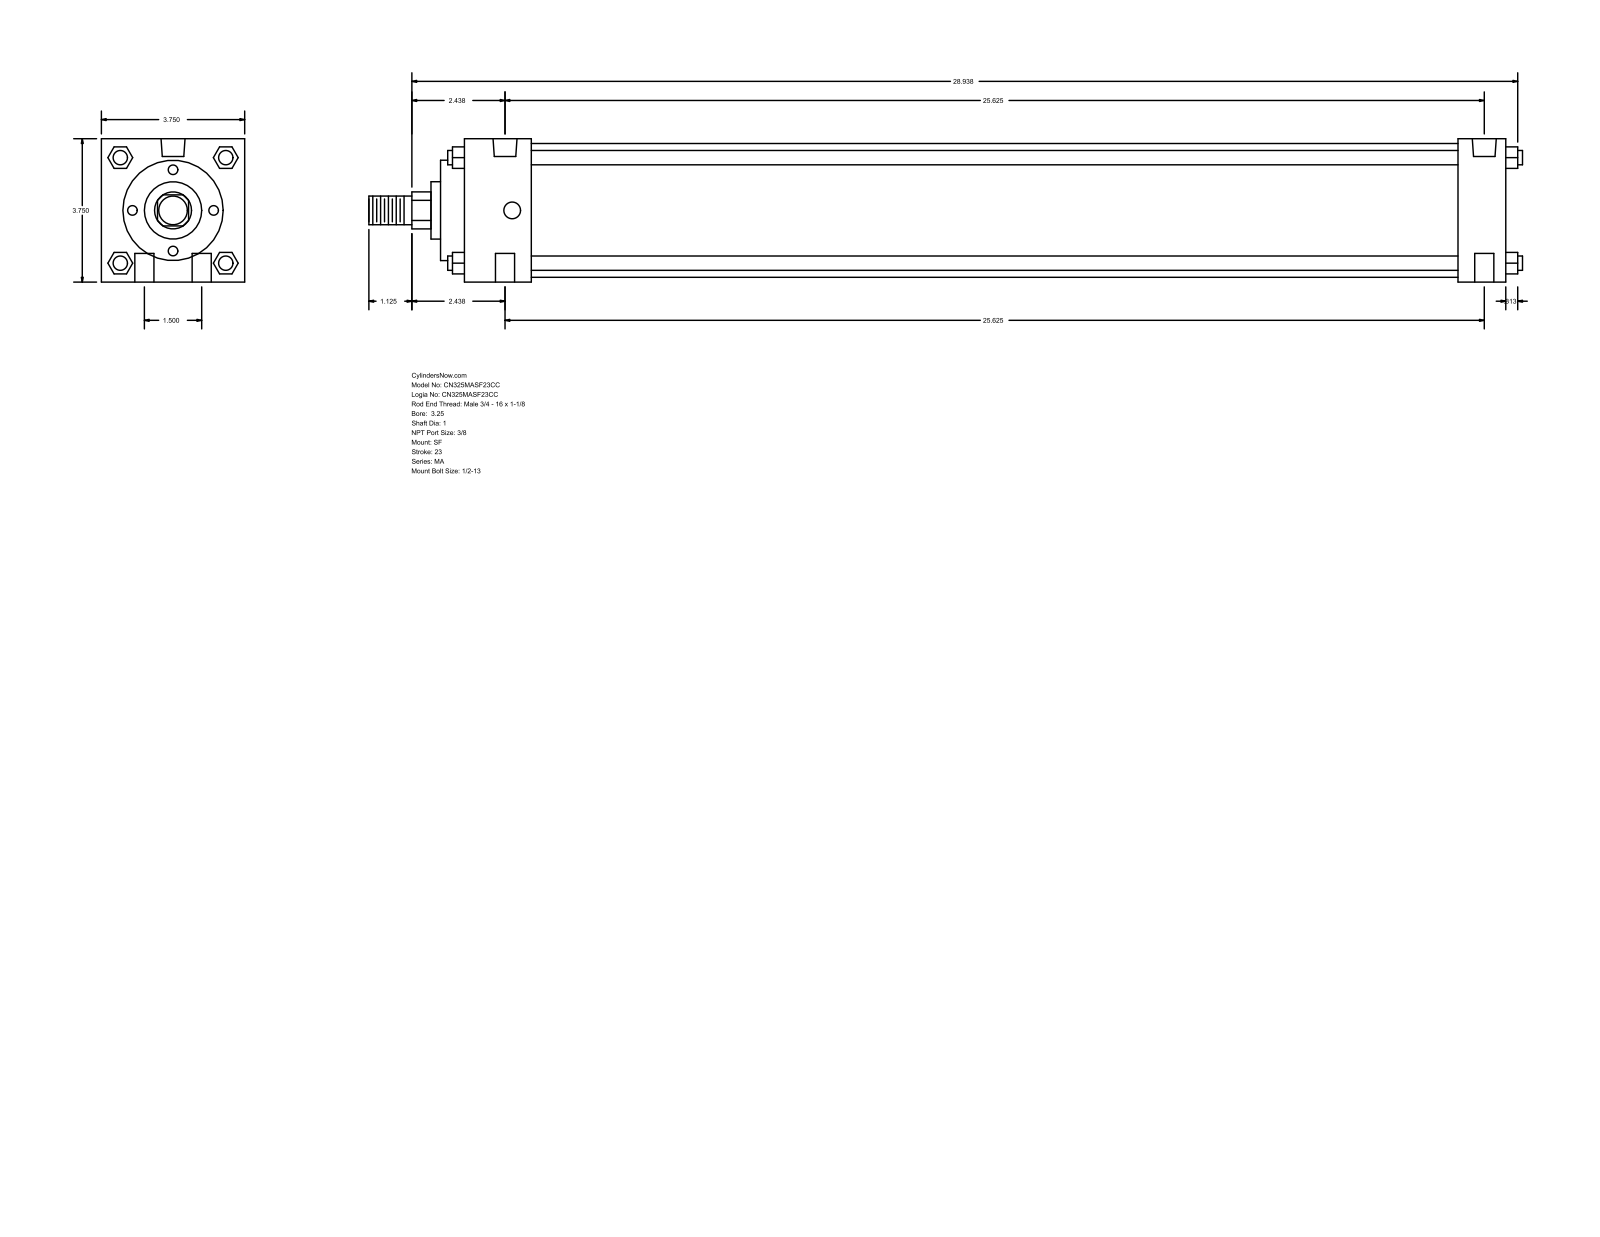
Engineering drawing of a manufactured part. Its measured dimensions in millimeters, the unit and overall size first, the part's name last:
Units: millimetres
Overall size (bounding box): 766.76 × 95.25 × 95.25
Round holes (diameter × count): ⌀12.7 ×4, ⌀11.11 ×2, ⌀15.93 ×2
Round bosses / shafts (diameter × count): ⌀9.53 ×4, ⌀88.9 ×1, ⌀66.67 ×1, ⌀38.1 ×1, ⌀25.4 ×1, ⌀19.05 ×1
Partial cylindrical surfaces — rounded edges, fillets, slot ends (radius × count): R12.29 ×1
Main face-to-face distances: 95.24, 692.16, 660.41, 31.75, 44.46, 615.95, 647.7, 15.87, 60.33, 676.28
Hole centre spacings: 19.05, 651.16, 650.88, 38.1, 651.99, 641.35
Bodies: 0 solids, 126 faces (95 planar, 31 cylindrical, 0 other)
Part name (STEP PRODUCT): MA_SF__0325_1
STEP written by: GSSL Pune (CONFIG_CONTROL_DESIGN)
